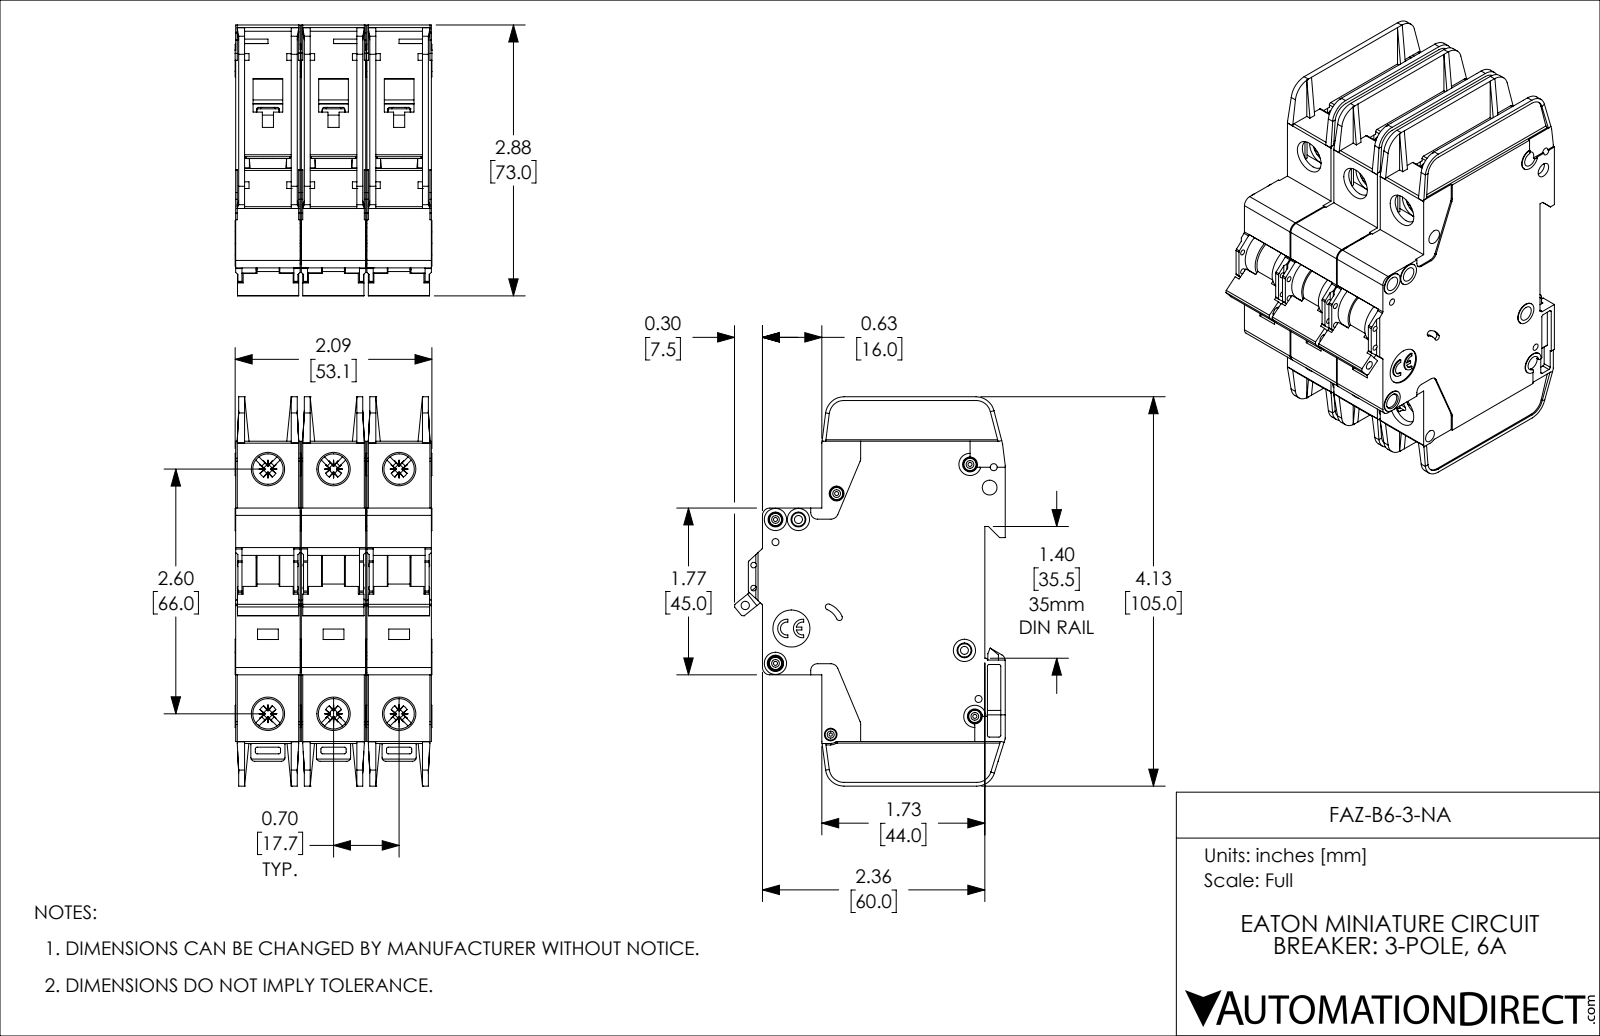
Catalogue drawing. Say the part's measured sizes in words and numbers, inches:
The part is named "FAZ-B6-3-NA". Its 3-D file was written by "SolidWorks 2019 (AUTOMOTIVE_DESIGN)". It is 3 solids with 3381 faces: 2013 planar, 1071 cylindrical and 297 other. Overall it measures 4.134 by 2.876 by 2.091 inches. Its volume is 14.05 cubic inches and its surface area 123 square inches. Round holes: 8 of diameter 0.157, 6 of diameter 0.323, 5 of diameter 0.043, 4 of diameter 0.075, 2 of diameter 0.059, 2 of diameter 0.085, 1 of diameter 0.035, 1 of diameter 0.089, 1 of diameter 0.098, 1 of diameter 0.134, 1 of diameter 0.394. Round bosses or shafts: 5 of diameter 0.13, 4 of diameter 0.236, 4 of diameter 0.118, 3 of diameter 0.098. Partial cylindrical surfaces (rounded edges, fillets, slot ends): 72 of radius 0.02, 30 of radius 0.016, 18 of radius 0.039, 12 of radius 0.043, 12 of radius 0.079, 6 of radius 0.008, 6 of radius 0.01, 6 of radius 0.028. The main face-to-face distances are 0.697, 0.047, 1.394, 0.685, 0.591, 1.382, 0.744, 0.65, 0.106, 0.094. The hole center spacings are 0.697, 2.69, 2.598, 0.244, 0.537, 0.87, 1.394, 2.948.
